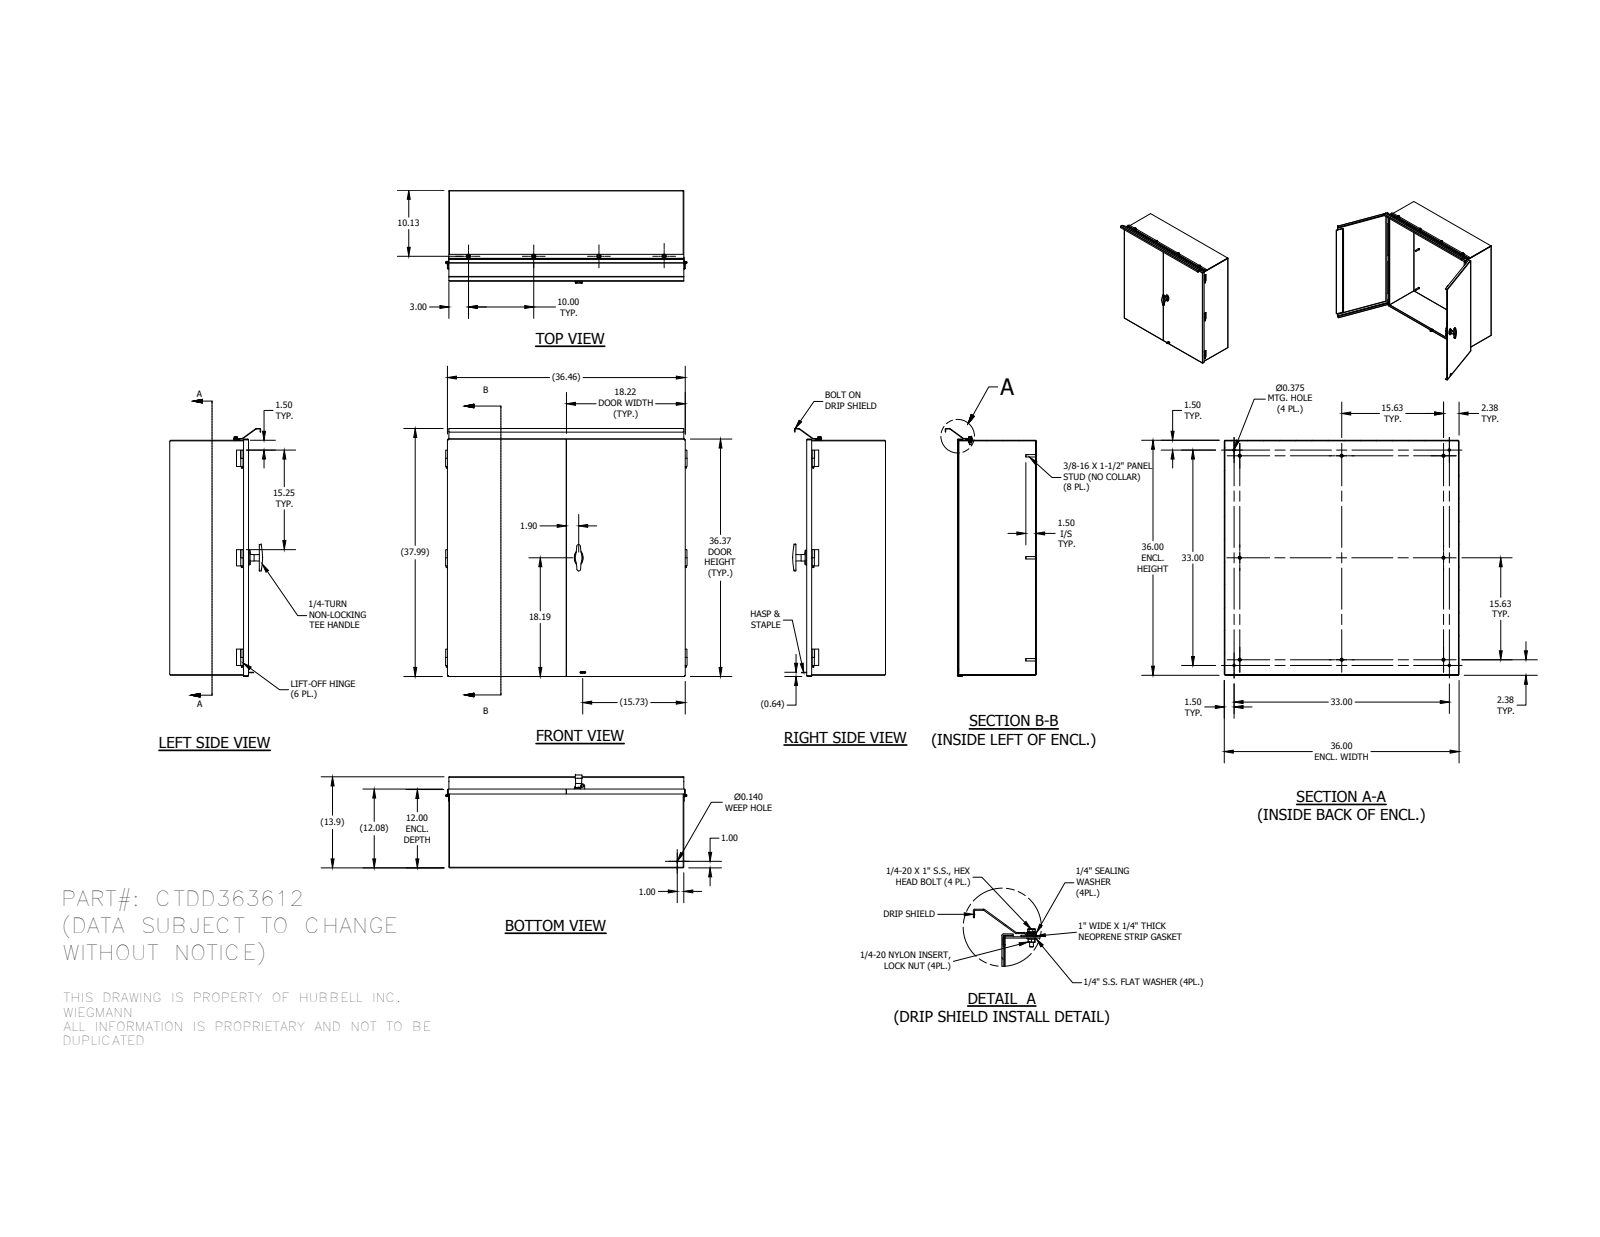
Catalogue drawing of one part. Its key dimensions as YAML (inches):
part_name: "CTDD363612BLR; CTDD3612TOP; CTDD3612BTM; 38822 (+8 more)"
step_written_by: "Autodesk Inventor 2014 (AUTOMOTIVE_DESIGN)"
units: inches
bodies: {solids: 67, faces: 1098, planar: 642, cylindrical: 230, other: 226}
overall_size: [37.995, 37, 14.235]
volume: 472.3
surface_area: 10160
round_holes:
  - {diameter: 0.196, count: 6}
  - {diameter: 0.281, count: 6}
  - {diameter: 0.375, count: 5}
  - {diameter: 0.235, count: 4}
  - {diameter: 0.275, count: 4}
  - {diameter: 0.29, count: 4}
  - {diameter: 0.16, count: 2}
  - {diameter: 0.211, count: 2}
  - {diameter: 0.219, count: 2}
  - {diameter: 0.25, count: 2}
  - {diameter: 0.281, count: 2}
  - {diameter: 0.094, count: 1}
round_bosses_or_shafts:
  - {diameter: 0.462, count: 8}
  - {diameter: 0.375, count: 8}
  - {diameter: 0.438, count: 6}
  - {diameter: 0.25, count: 6}
  - {diameter: 0.65, count: 4}
  - {diameter: 0.625, count: 4}
  - {diameter: 0.6, count: 4}
  - {diameter: 0.26, count: 4}
partial_cylinders:
  - {radius: 0.031, count: 23}
  - {radius: 0.125, count: 13}
  - {radius: 0.105, count: 6}
  - {radius: 0.125, count: 6}
  - {radius: 0.063, count: 3}
  - {radius: 0.063, count: 3}
  - {radius: 0.008, count: 2}
  - {radius: 0.156, count: 2}
face_to_face_distances: [0.094, 11.984, 11.891, 12.078, 35.906, 36, 0.093, 35.813, 35.813, 35.907]
hole_center_spacings: [33, 10, 0.75, 20, 21.485, 22.041, 22.608, 24.21]
